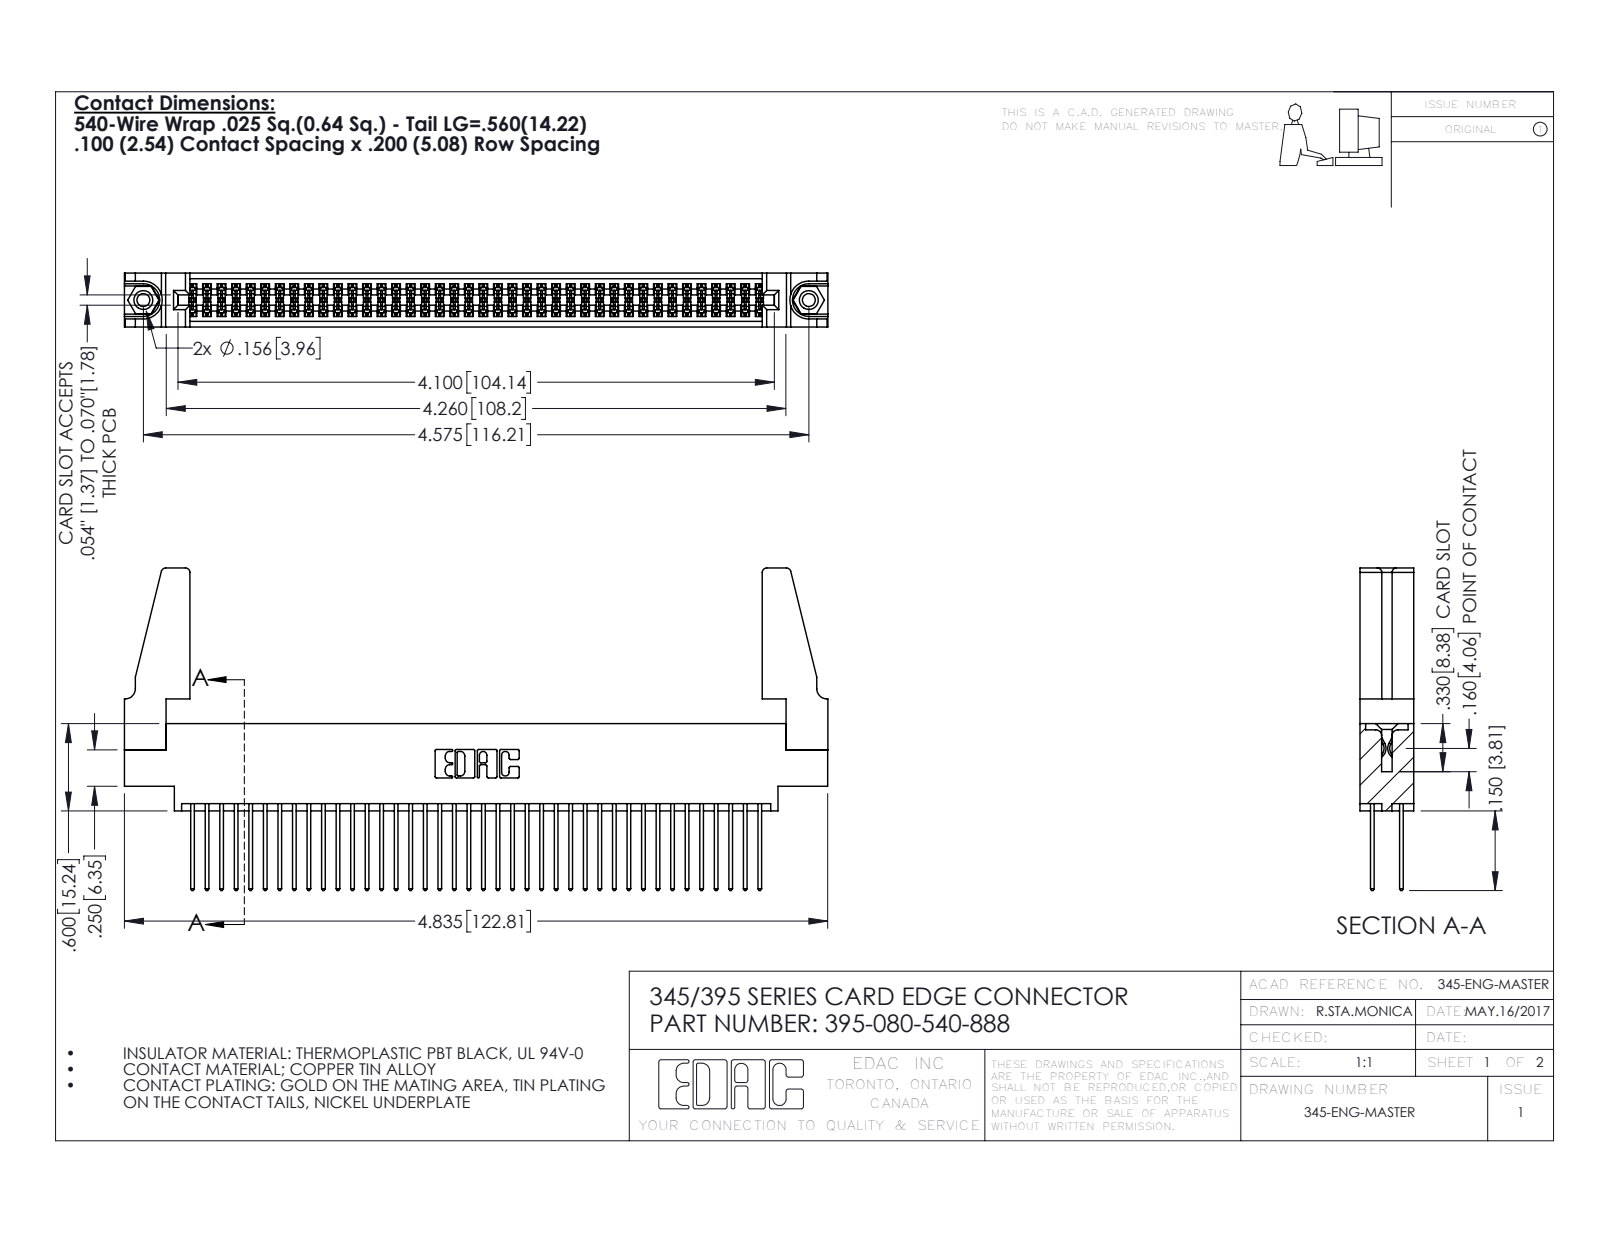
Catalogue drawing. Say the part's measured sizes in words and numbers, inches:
The part is named "345-292-001_345-293-140; 345 Part_0.170 Offset - 0.156 Dia-TH; 345-250-001_345-250-001-102; 345-220-078_345-220-088 (+1 more)". Its 3-D file was written by "SolidWorks 2016 (CONFIG_CONTROL_DESIGN)". It is 85 solids with 4254 faces: 2796 planar, 1442 cylindrical and 16 other. Overall it measures 4.836 by 2.217 by 0.37 inches. Its volume is 0.937 cubic inches and its surface area 34.91 square inches. Round holes: 2 of diameter 0.089, 2 of diameter 0.125, 2 of diameter 0.156, 1 of diameter 0.064. Round bosses or shafts: 2 of diameter 0.155. Partial cylindrical surfaces (rounded edges, fillets, slot ends): 120 of radius 0.006, 80 of radius 0.01, 22 of radius 0.01, 8 of radius 0.03, 6 of radius 0.007, 6 of radius 0.031, 3 of radius 0.026, 2 of radius 0.014. The main face-to-face distances are 0.072, 0.298, 0.37, 0.2, 0.098, 0.272, 0.025, 0.225, 0.175, 0.149. The hole center spacings are 0.27, 4.339, 4.575.
